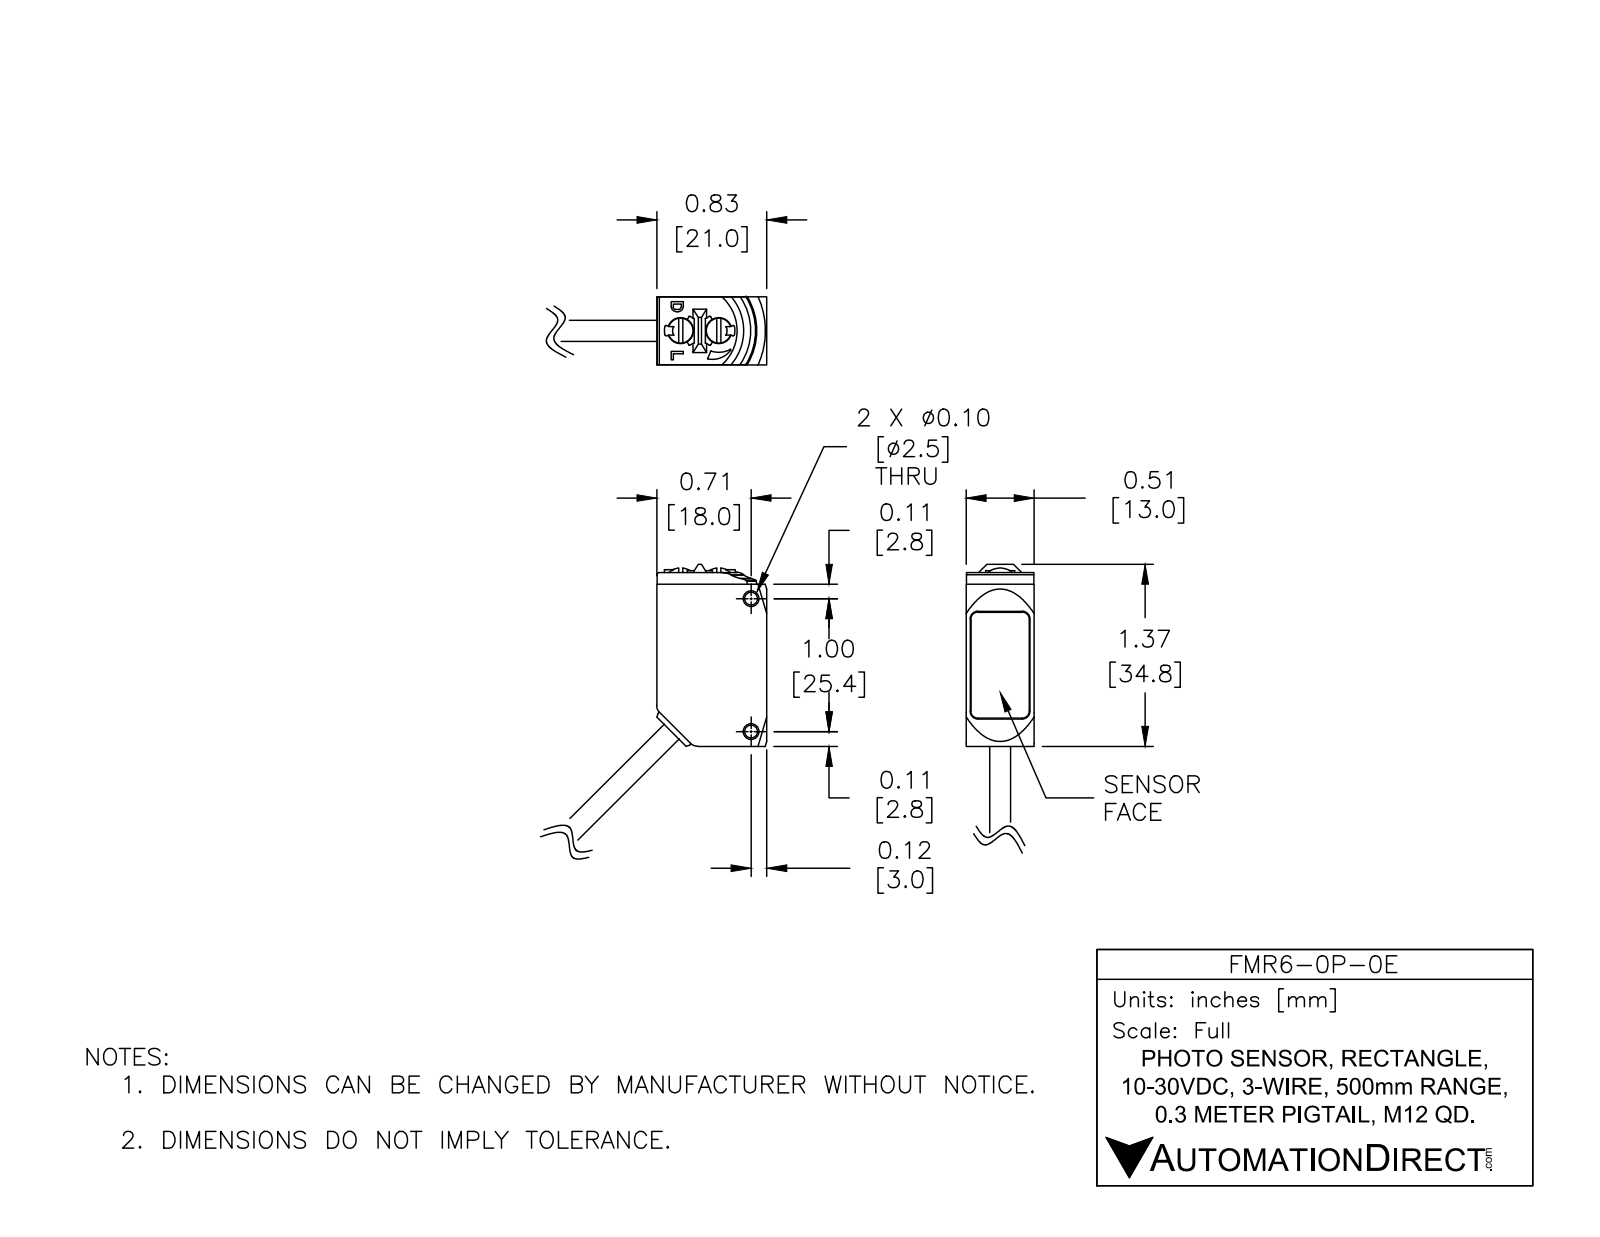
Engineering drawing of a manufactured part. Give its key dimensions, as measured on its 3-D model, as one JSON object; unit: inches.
{"part_name": "FMR6-0P-0E", "step_written_by": "SolidWorks 2017 (AUTOMOTIVE_DESIGN)", "units": "inches", "bodies": {"solids": 1, "faces": 186, "planar": 89, "cylindrical": 72, "other": 25}, "overall_size": [2.084, 1.541, 0.512], "volume_in3": 0.542, "surface_area_in2": 5.476, "round_holes": [[0.097, 2], [0.197, 2]], "round_bosses_or_shafts": [[0.189, 2], [0.157, 1]], "partial_cylinders_radius": [[0.018, 7], [0.02, 7], [0.008, 4], [0.01, 4], [0.051, 4], [0.059, 4], [0.004, 3], [0.018, 2]], "face_to_face_distances": [0.512, 0.827, 1.307, 0.035, 0.51, 0.031, 0.48, 0.037, 0.474, 0.472], "hole_center_spacings": [0.287, 1]}
